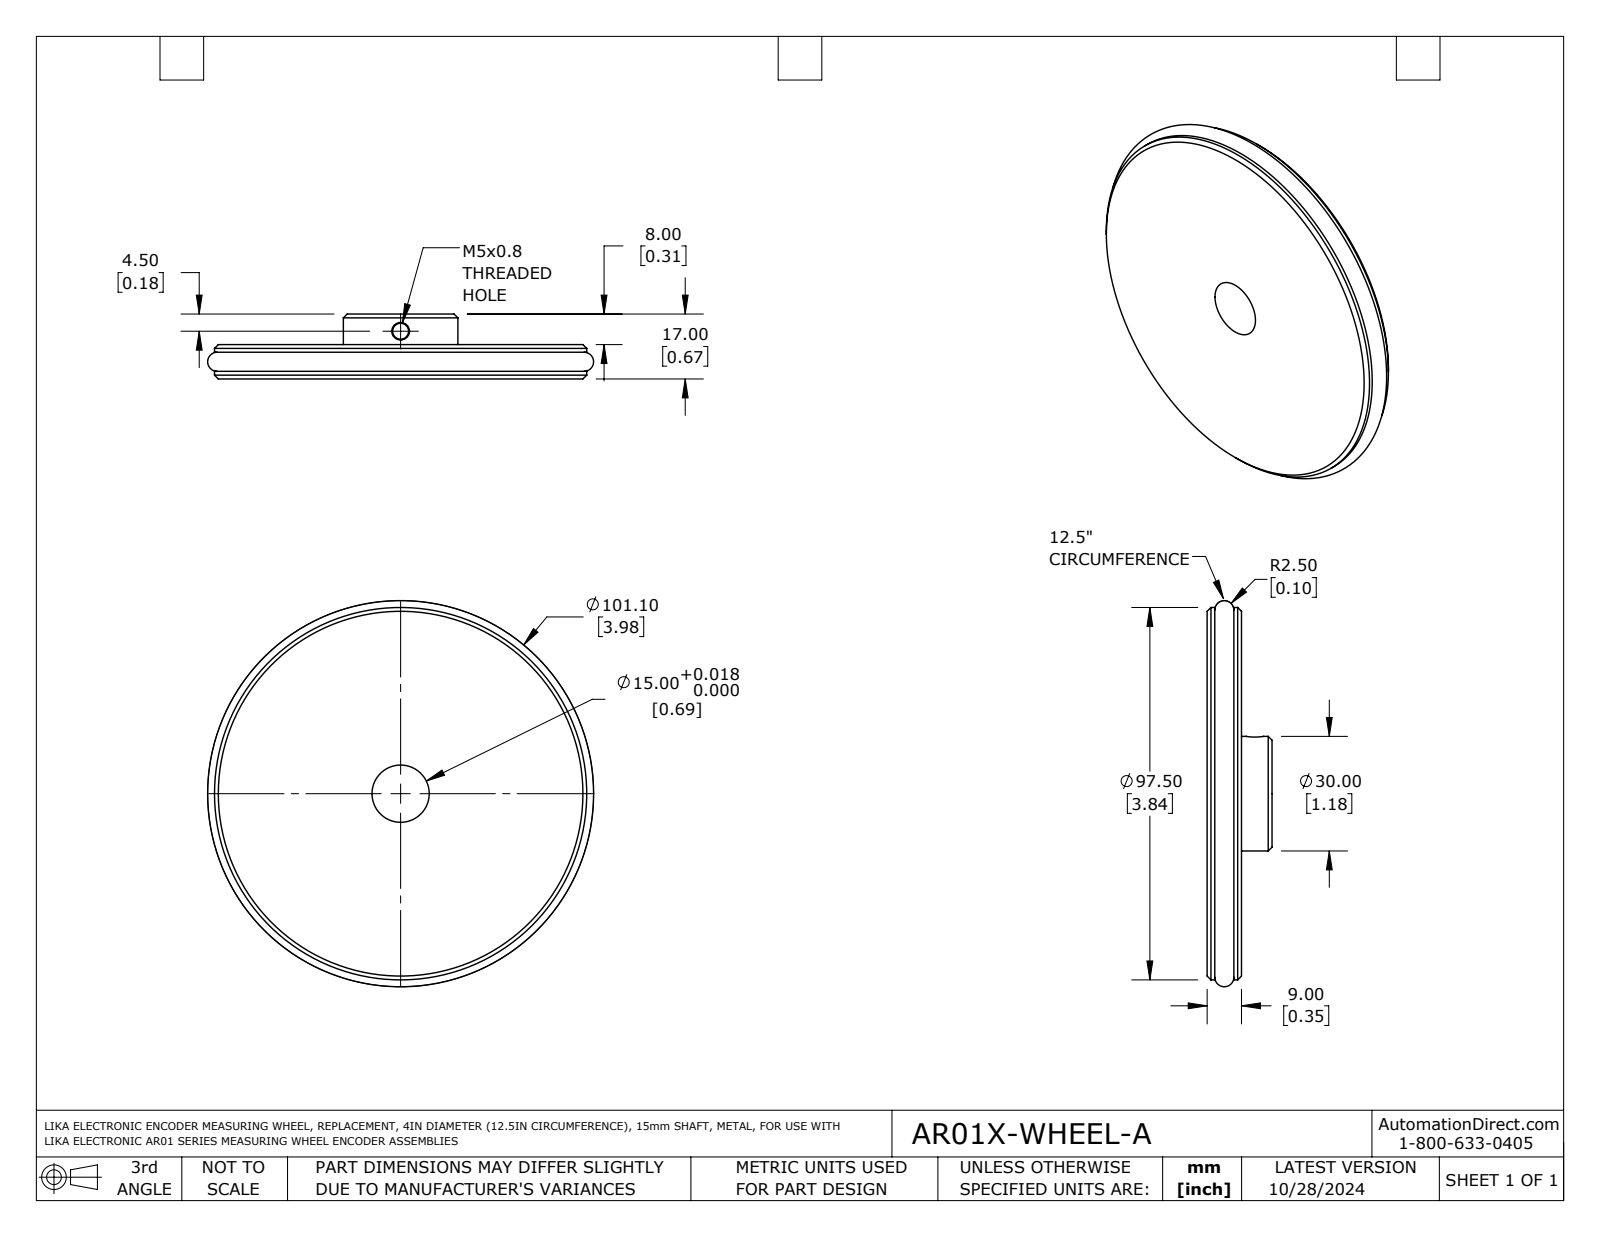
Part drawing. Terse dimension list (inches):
name: AR01X-WHEEL-A
written by: SolidWorks 2021 (AUTOMOTIVE_DESIGN)
unit: in
bodies: 2 solids, 40 faces (6 planar, 14 cylindrical, 20 other)
size: 3.98 × 3.98 × 0.669
volume: 3.052 in³; area: 40.41 in²
holes: 1× ⌀0.165, 1× ⌀0.591, 1× ⌀3.15
bosses: 1× ⌀3.839, 1× ⌀3.594, 1× ⌀1.181
face distances: 0.157, 0.197, 0.354, 0.079, 0.276, 0.118, 0.315, 0.394, 0.512, 0.591
